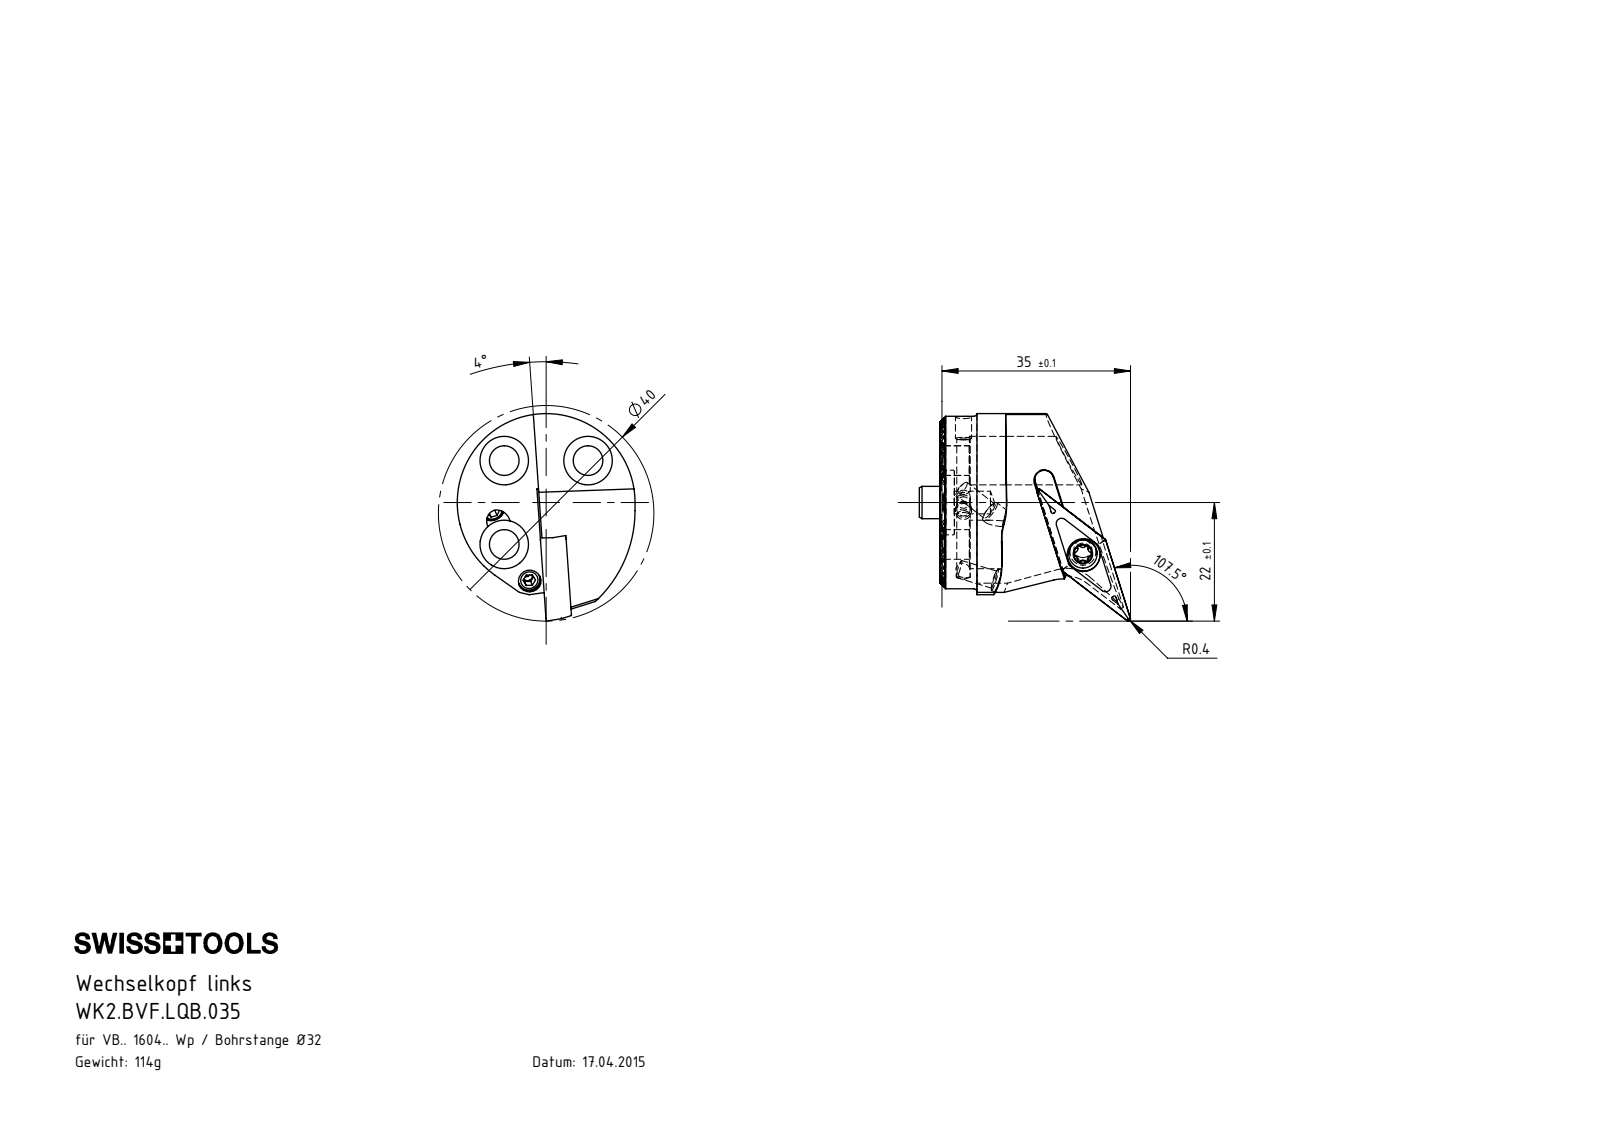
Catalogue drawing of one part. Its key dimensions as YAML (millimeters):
part_name: "KVT_MB_600_030; VBMT160404; WK2.BVF.LQB.035; WKX-ER1.004.005_A_PreviewCfg (+3 more)"
step_written_by: "SolidWorks 2017 (AUTOMOTIVE_DESIGN)"
units: millimeters
bodies: {solids: 10, faces: 532, planar: 198, cylindrical: 186, other: 148}
overall_size: [39.2, 38.5, 33]
volume: 14059
surface_area: 8053
round_holes:
  - {diameter: 3.3, count: 3}
  - {diameter: 4.2, count: 3}
  - {diameter: 5.5, count: 3}
  - {diameter: 9, count: 3}
  - {diameter: 1.7, count: 2}
  - {diameter: 2.38, count: 2}
  - {diameter: 2.5, count: 2}
  - {diameter: 3, count: 2}
  - {diameter: 4.4, count: 1}
  - {diameter: 6.1, count: 1}
  - {diameter: 12, count: 1}
round_bosses_or_shafts:
  - {diameter: 4, count: 3}
  - {diameter: 3, count: 2}
  - {diameter: 32, count: 1}
  - {diameter: 6, count: 1}
  - {diameter: 5.25, count: 1}
partial_cylinders:
  - {radius: 0.12, count: 22}
  - {radius: 0.34, count: 6}
  - {radius: 0.59, count: 6}
  - {radius: 12, count: 3}
  - {radius: 0.15, count: 2}
  - {radius: 1.75, count: 1}
  - {radius: 7, count: 1}
  - {radius: 16.5, count: 1}
face_to_face_distances: [1.3, 2.6, 3.9, 5.2, 6.5, 12.99, 11.69, 4.46, 14.29, 7.8]
hole_center_spacings: [11, 15.56, 22.01]
